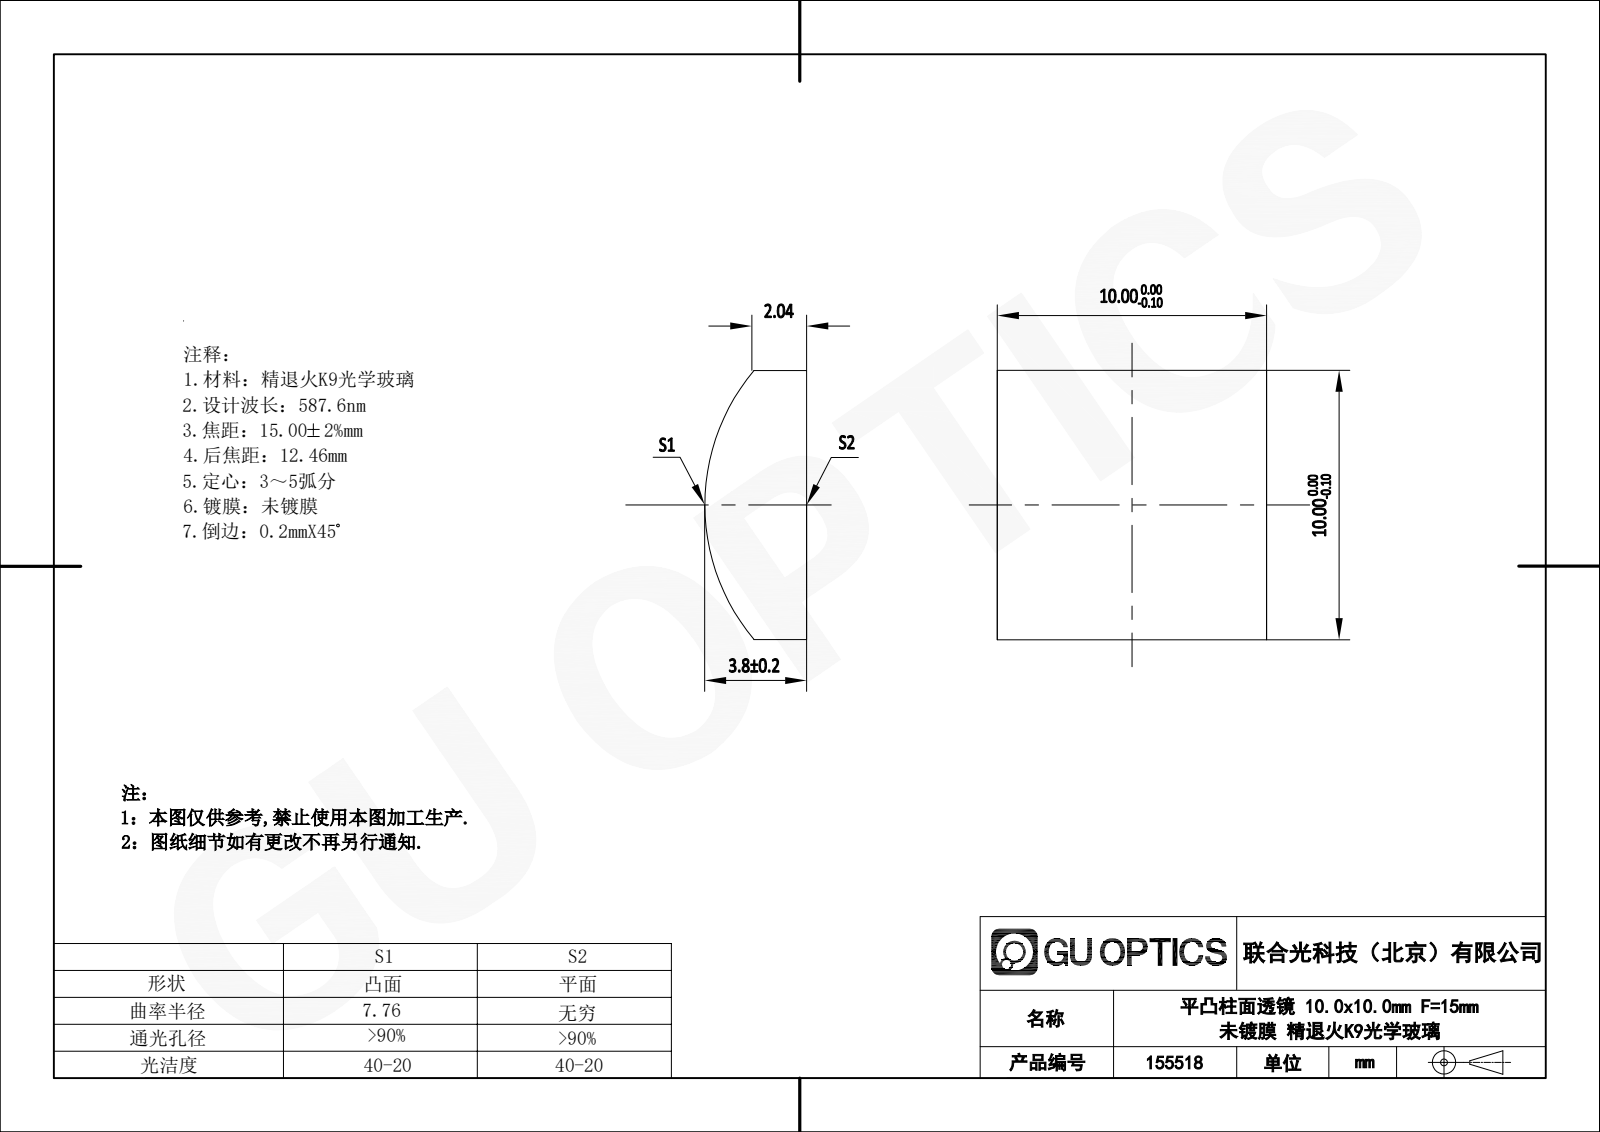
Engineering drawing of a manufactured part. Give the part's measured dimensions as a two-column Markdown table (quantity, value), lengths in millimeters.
| quantity | value |
| --- | --- |
| part name | 155518 |
| STEP written by | SolidWorks 2020 (CONFIG_CONTROL_DESIGN) |
| units | millimeters |
| bodies | 1 solid, 7 faces (5 planar, 2 cylindrical, 0 other) |
| overall size | 10 × 10 × 3.8 |
| volume | 322 mm³ |
| surface area | 312 mm² |
| partial cylindrical surfaces (radius × count) | 7.76 × 1 |
| main face-to-face distances | 10 |
